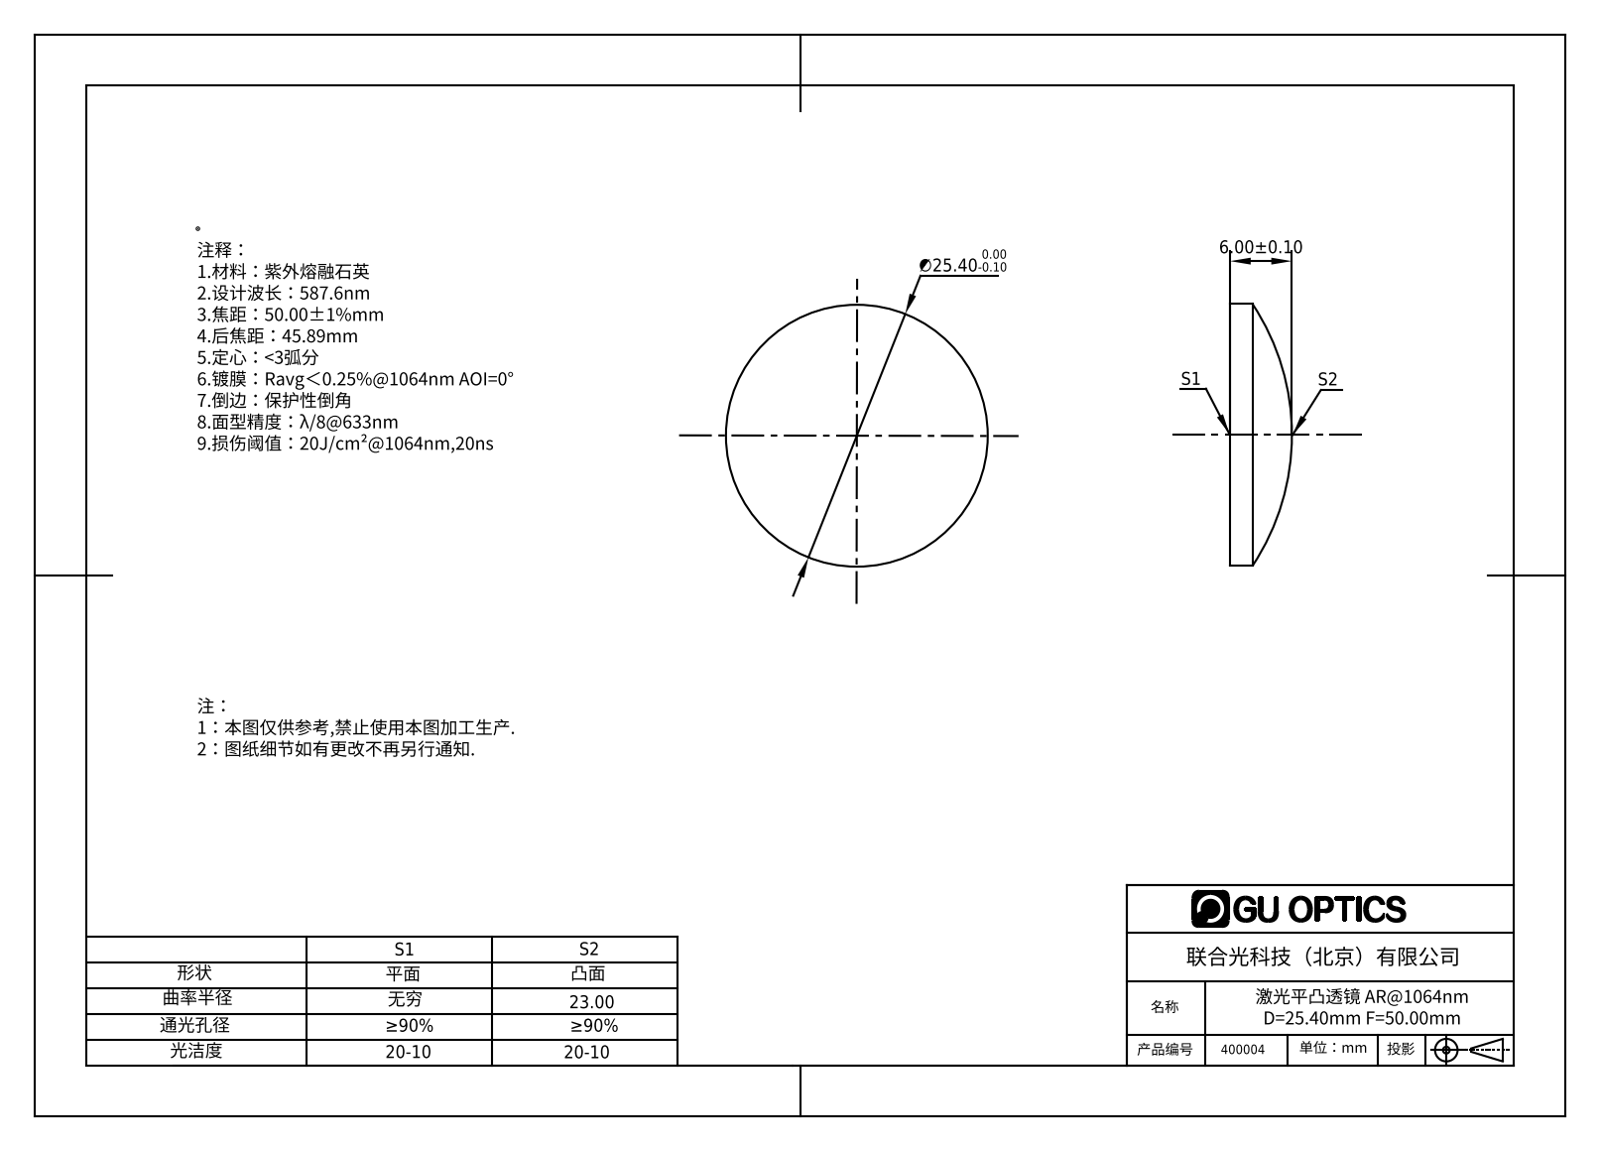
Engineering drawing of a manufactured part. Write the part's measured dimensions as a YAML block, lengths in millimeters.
part_name: "400004"
step_written_by: "SolidWorks 2016 (AUTOMOTIVE_DESIGN)"
units: millimeters
bodies: {solids: 1, faces: 5, planar: 1, cylindrical: 2, other: 2}
overall_size: [25.4, 25.4, 6]
volume: 2101
surface_area: 1233
round_bosses_or_shafts:
  - {diameter: 25.4, count: 1}
